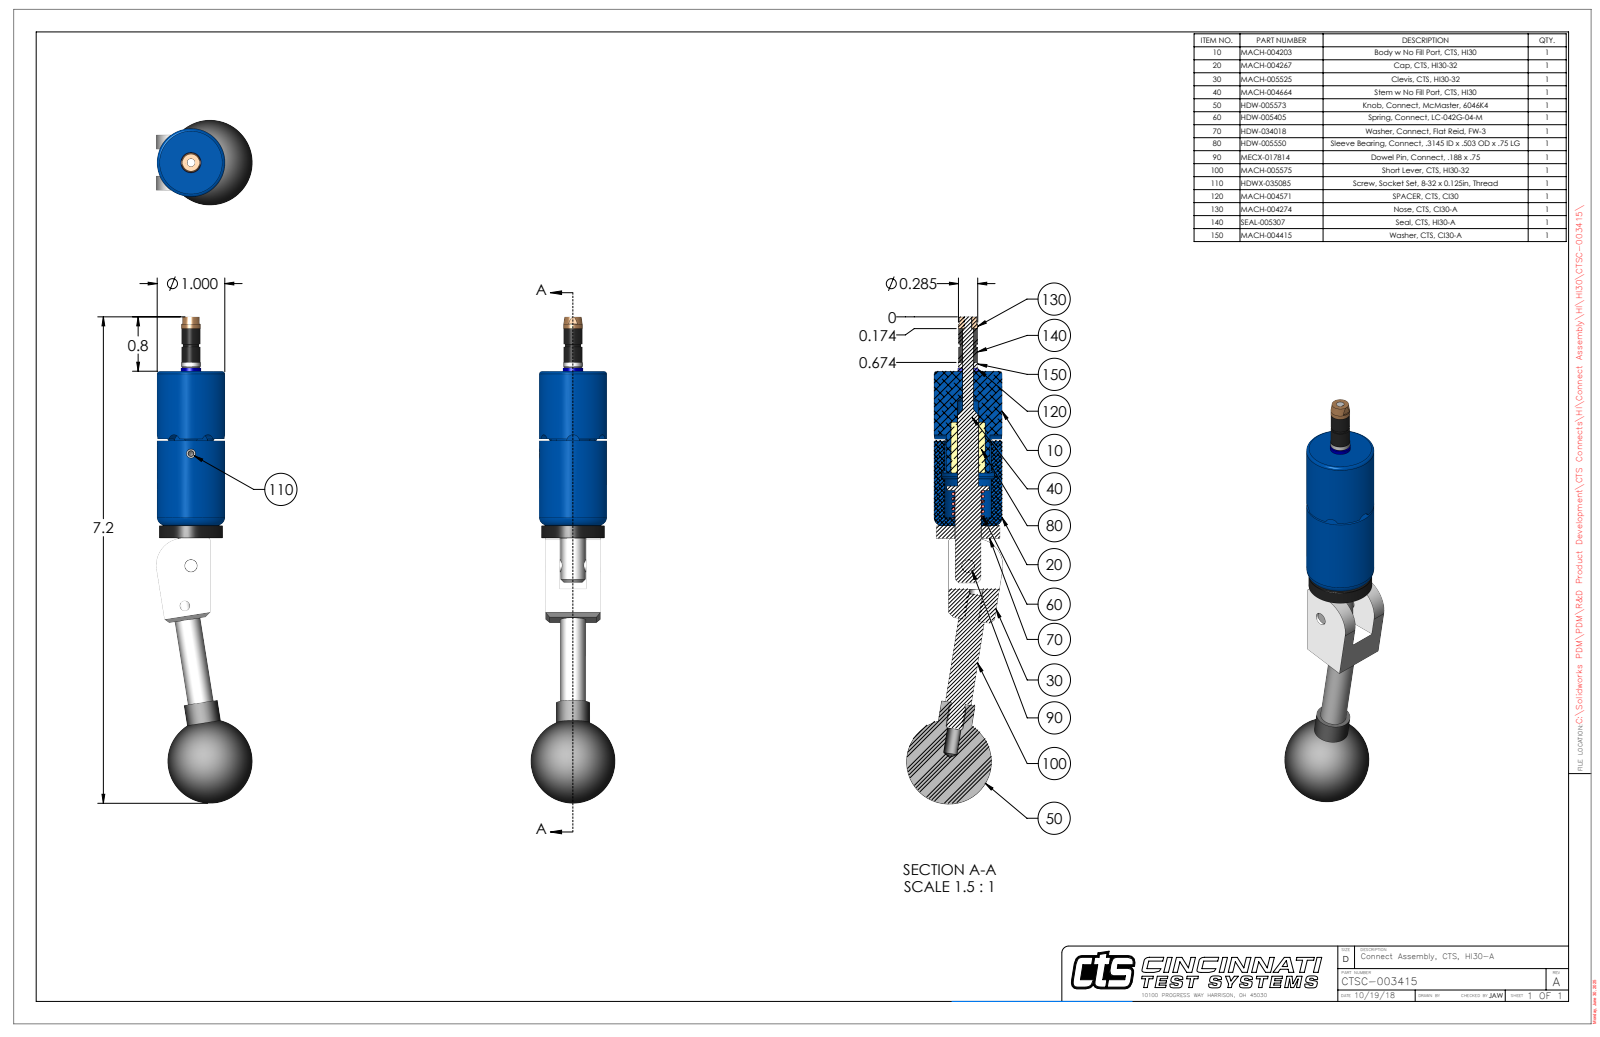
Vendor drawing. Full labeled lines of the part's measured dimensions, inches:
Part name (STEP PRODUCT): CTSC-003415
STEP written by: SolidWorks 2023 (AUTOMOTIVE_DESIGN)
Units: inches
Bodies: 11 solids, 264 faces (102 planar, 101 cylindrical, 61 other)
Overall size (bounding box): 7.193 × 1.416 × 1.25
Volume: 3.704 in³ · Surface area: 28.82 in²
Round holes (diameter × count): ⌀0.201 ×2, ⌀0.113 ×1, ⌀0.136 ×1, ⌀0.15 ×1, ⌀0.155 ×1, ⌀0.161 ×1, ⌀0.164 ×1, ⌀0.189 ×1, ⌀0.385 ×1, ⌀0.392 ×1
Round bosses / shafts (diameter × count): ⌀1 ×1, ⌀0.936 ×1, ⌀0.5 ×1, ⌀0.38 ×1, ⌀0.375 ×1, ⌀0.3 ×1, ⌀0.288 ×1, ⌀0.285 ×1
Partial cylindrical surfaces — rounded edges, fillets, slot ends (radius × count): R0.093 ×6, R0.015 ×1, R0.344 ×1, R0.4 ×1, R0.451 ×1
Main face-to-face distances: 0.21, 0.602, 0.812, 0.187, 2.28, 2.467, 0.391, 1.026, 1.253, 1.441
Hole centre spacings: 0.599, 1.658, 2.252
